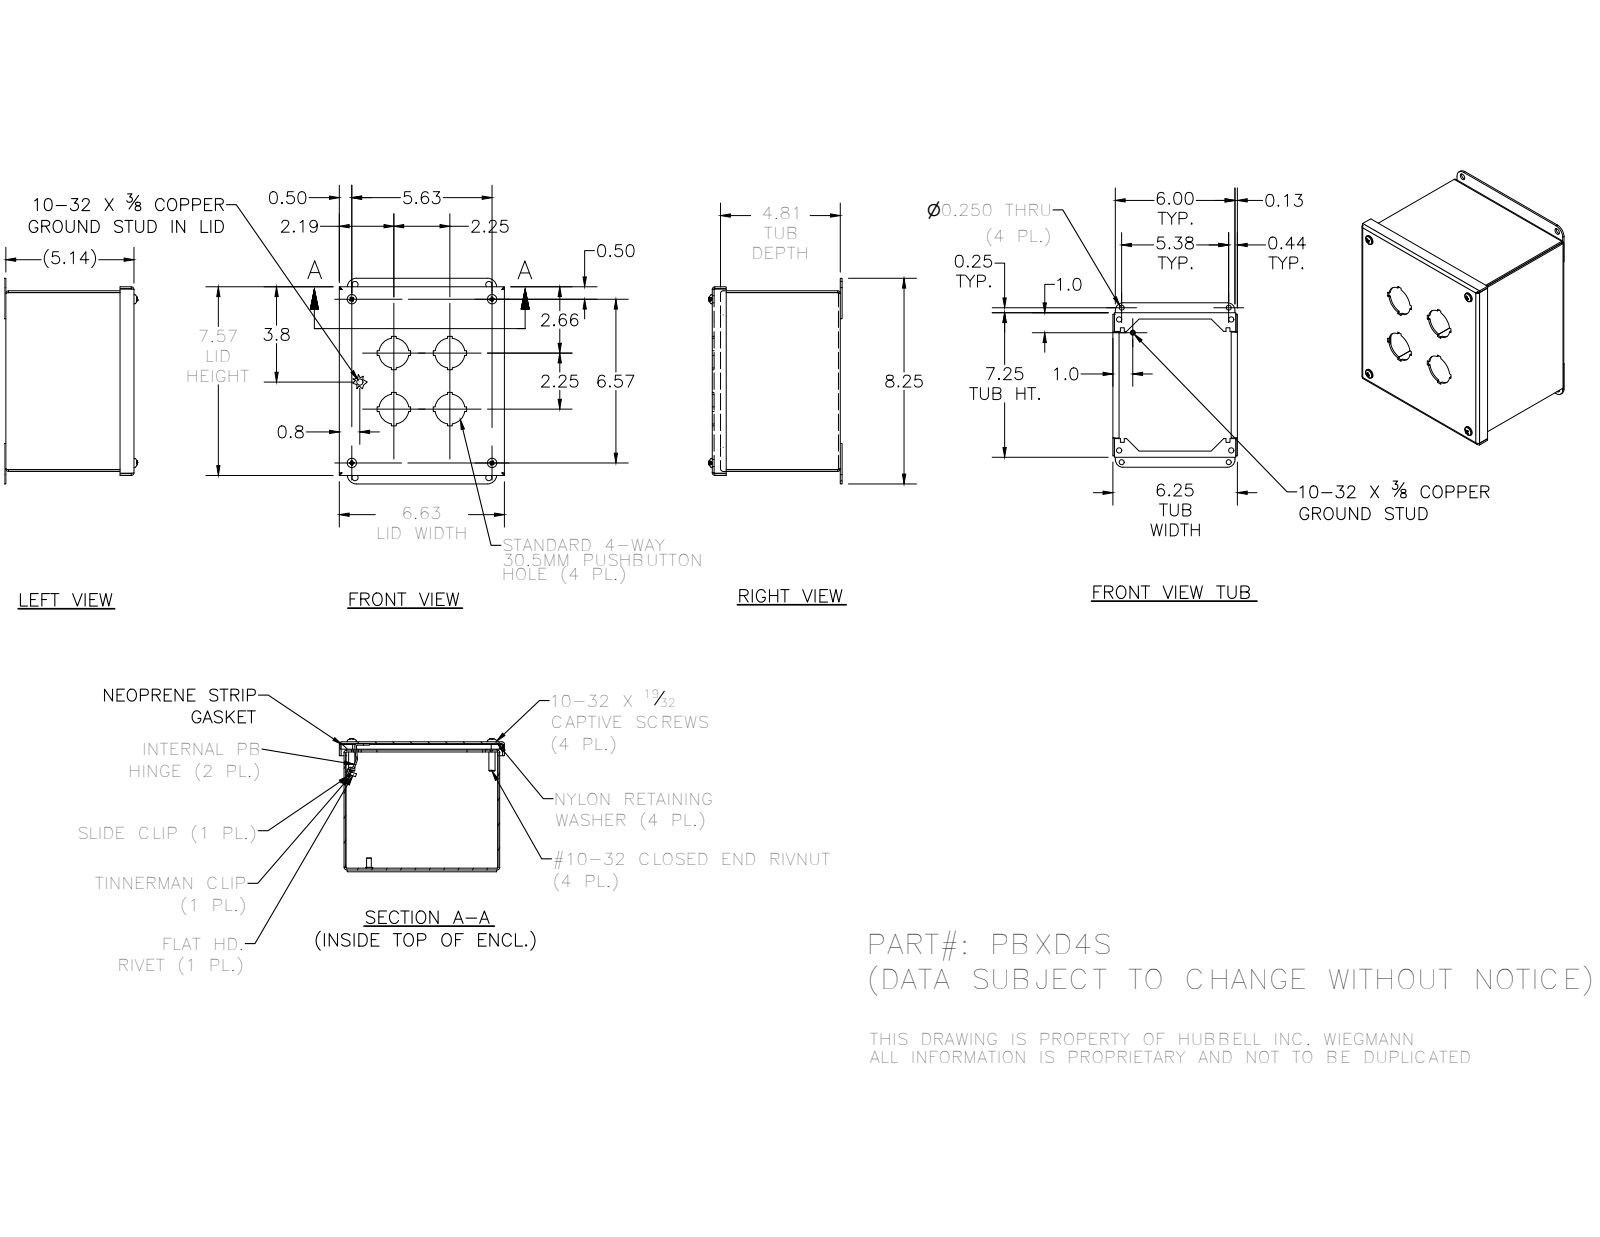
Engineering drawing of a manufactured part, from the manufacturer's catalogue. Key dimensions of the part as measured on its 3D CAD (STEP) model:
Part name (STEP PRODUCT): PBXD4SLID; 372163; 39077; PBXD4SBKP (+8 more)
STEP written by: Autodesk Inventor 2016 (AUTOMOTIVE_DESIGN)
Units: millimetres
Bodies: 25 solids, 673 faces (411 planar, 148 cylindrical, 114 other)
Overall size (bounding box): 209.55 × 168.4 × 135.79
Volume: 363 382 mm³ · Surface area: 374 391 mm²
Round holes (diameter × count): ⌀3.96 ×4, ⌀4.98 ×4, ⌀6.35 ×4, ⌀6.53 ×4, ⌀7.06 ×4, ⌀7.14 ×4, ⌀7.95 ×4, ⌀30.48 ×4, ⌀3.56 ×2
Round bosses / shafts (diameter × count): ⌀4.83 ×6, ⌀11.51 ×4, ⌀10.31 ×4, ⌀9.47 ×4, ⌀6.3 ×4, ⌀6.35 ×3, ⌀3.17 ×1
Partial cylindrical surfaces — rounded edges, fillets, slot ends (radius × count): R0.79 ×12, R2.67 ×12, R4.78 ×6, R2.27 ×4, R2.29 ×4, R9.53 ×4, R0.8 ×3, R1.59 ×3
Main face-to-face distances: 1.88, 128.73, 156.87, 130.61, 182.27, 126.85, 154.99, 158.75, 184.15, 180.39
Hole centre spacings: 57.15, 80.34, 133.06, 181.89, 1.3, 2.1, 13.78, 15.33
